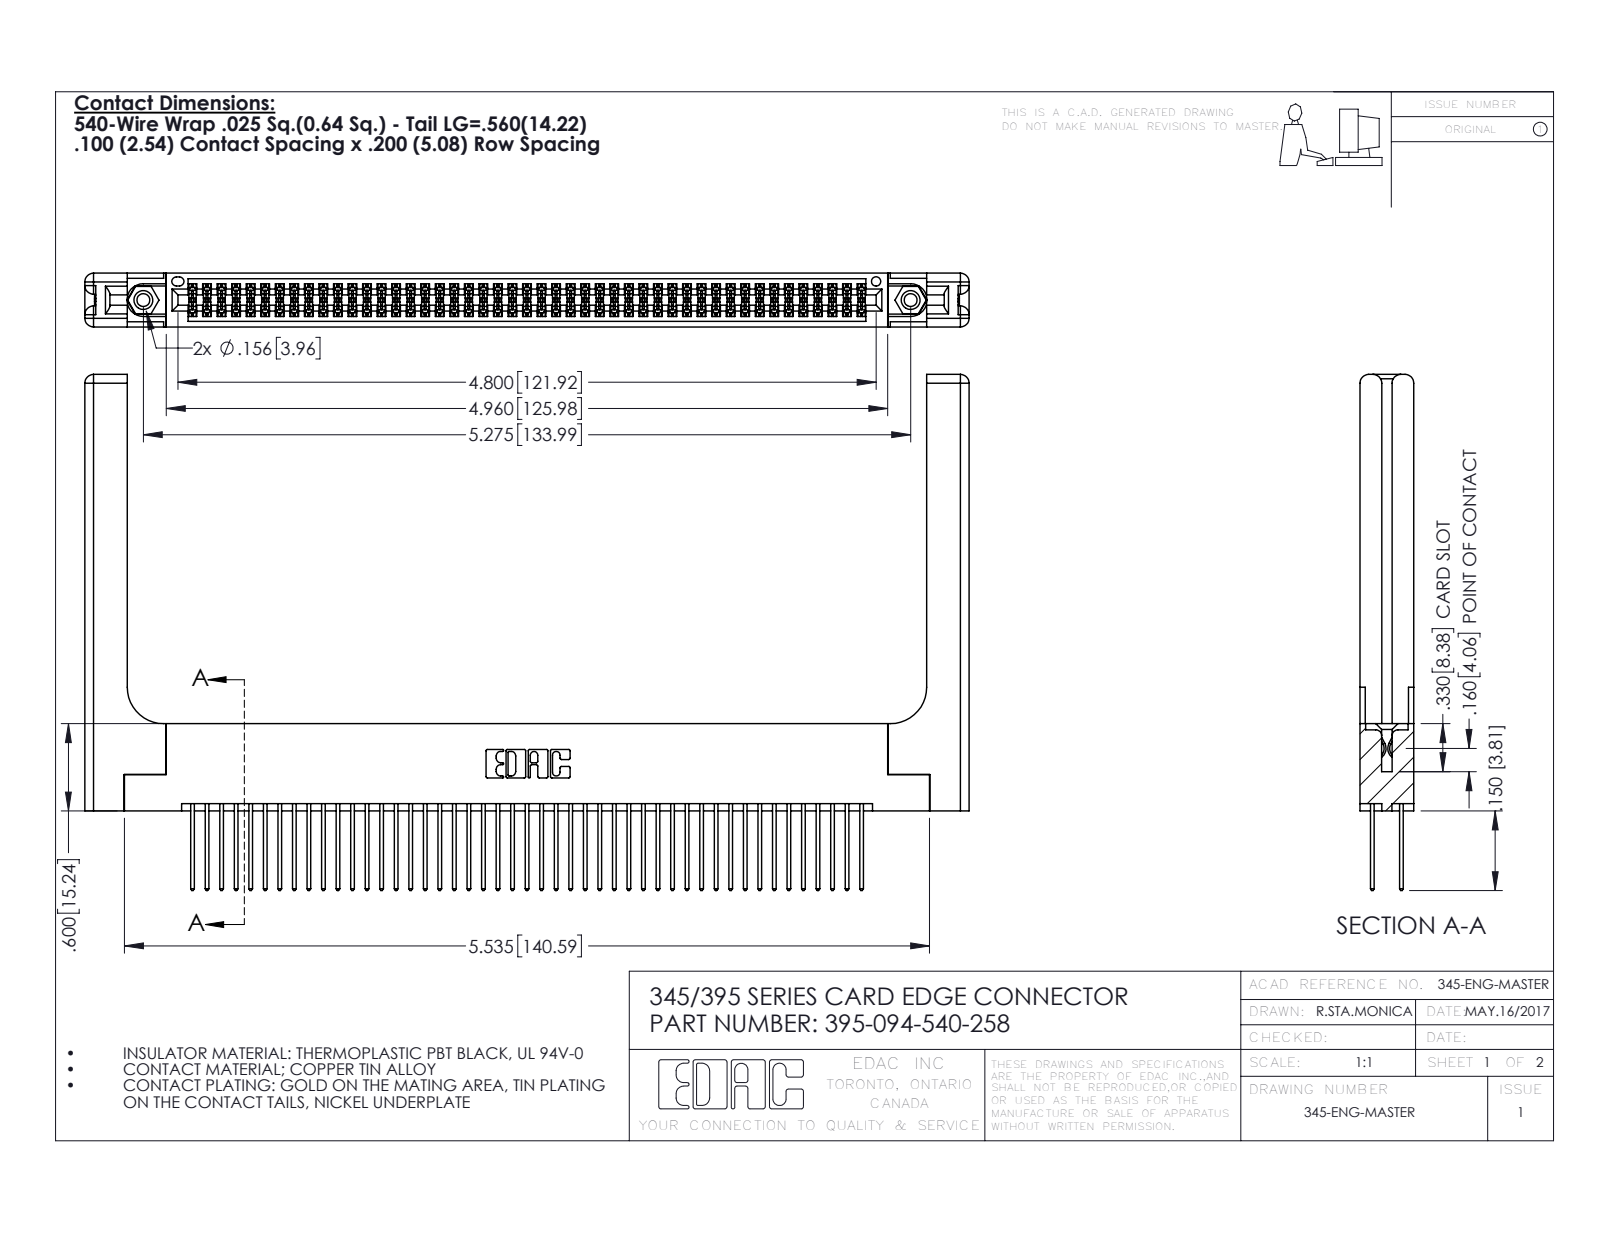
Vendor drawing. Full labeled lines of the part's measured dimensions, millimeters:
Part name (STEP PRODUCT): 345-220-058_345-220-058; 395-094-540-258; 345-292-001_345-293-140; 345 Part_Flush Mounting Lugs - 0.156 Dia-TH (+1 more)
STEP written by: SolidWorks 2016 (CONFIG_CONTROL_DESIGN)
Units: millimetres
Bodies: 99 solids, 5082 faces (3330 planar, 1692 cylindrical, 60 other)
Overall size (bounding box): 154.4 × 90.1 × 9.4
Volume: 23 880 mm³ · Surface area: 29 570 mm²
Round holes (diameter × count): ⌀2.3 ×2, ⌀3.2 ×2, ⌀4 ×2, ⌀1.6 ×1
Round bosses / shafts (diameter × count): ⌀3.9 ×2
Partial cylindrical surfaces — rounded edges, fillets, slot ends (radius × count): R0.2 ×141, R0.3 ×94, R0.3 ×22, R1.5 ×16, R0.2 ×6, R0.8 ×6, R0.7 ×3, R0.4 ×2
Main face-to-face distances: 1.8, 7.6, 9.4, 5.1, 2.5, 6.9, 0.6, 5.7, 4.4, 3.8
Hole centre spacings: 6.9, 128, 134
